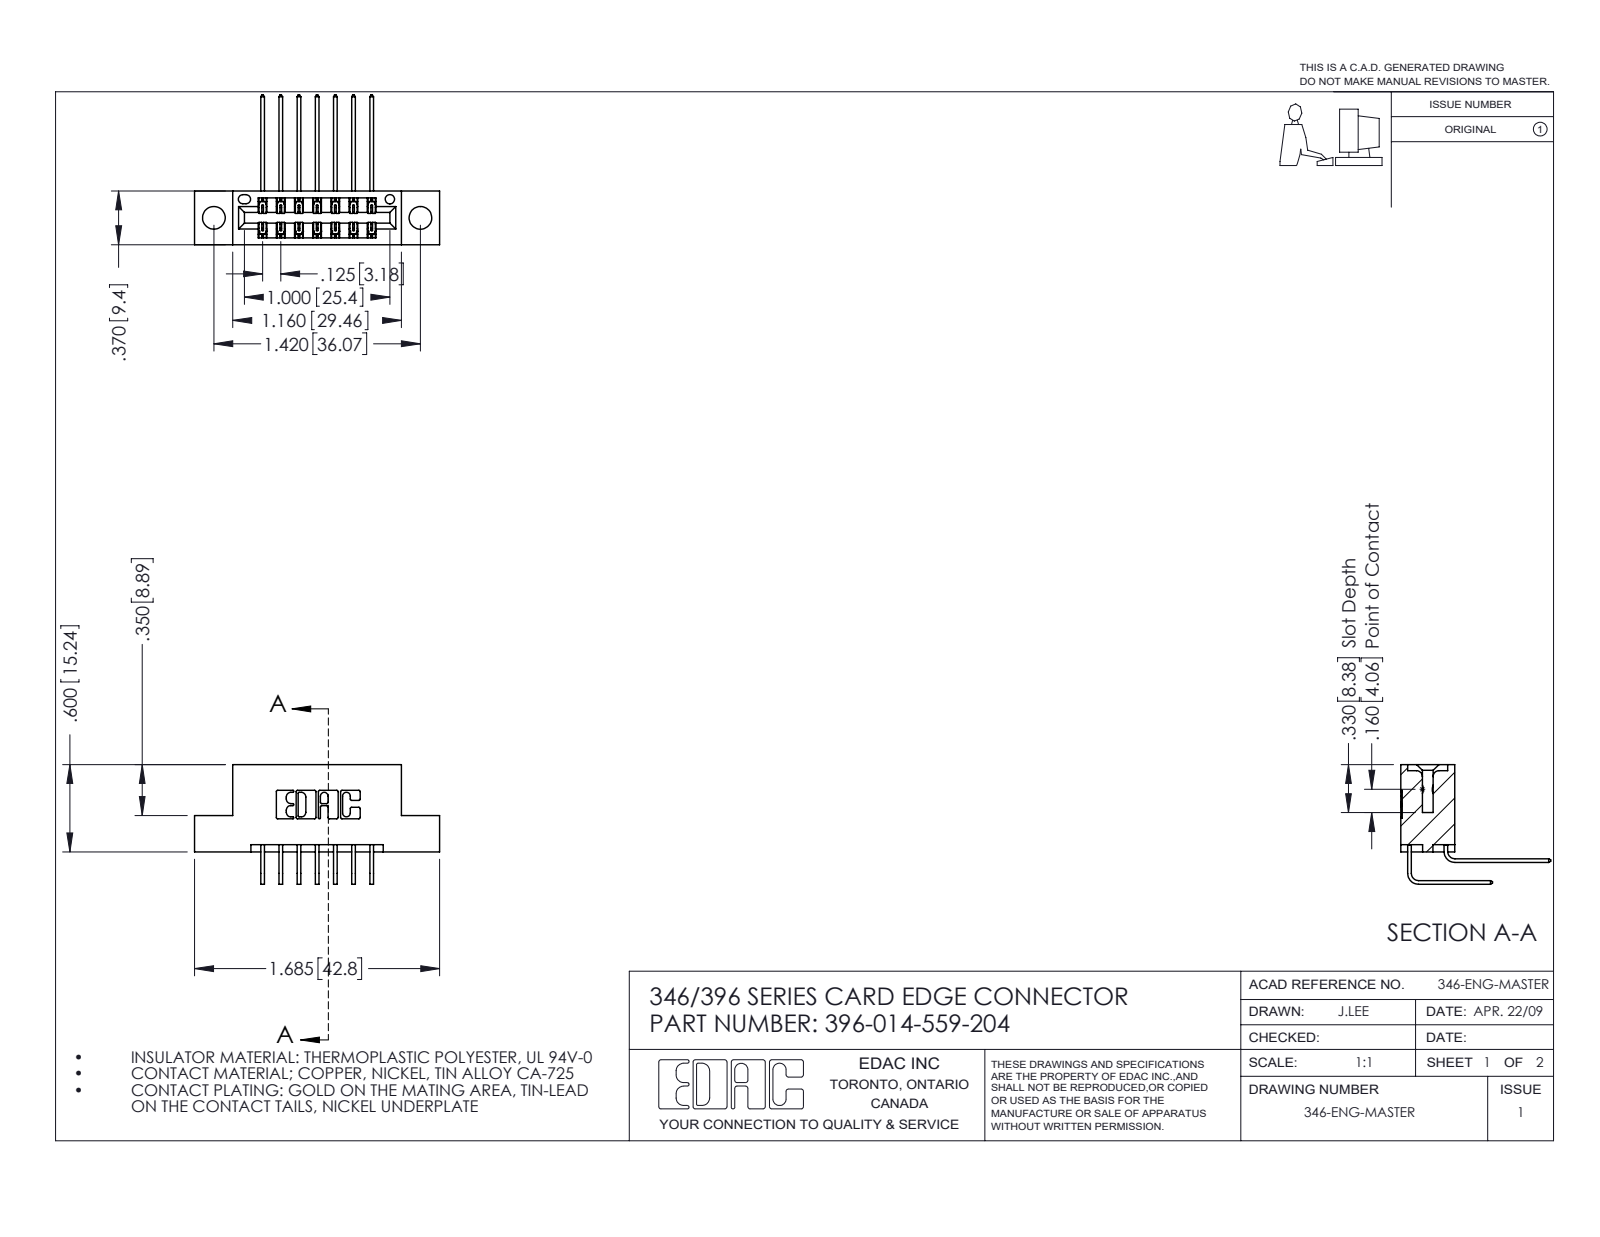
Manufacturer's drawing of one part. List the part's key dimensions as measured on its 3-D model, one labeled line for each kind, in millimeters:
Part name (STEP PRODUCT): 346 Part_Flush Mounting Lugs - 0.156 Dia-TH; 345-292-001_558 559 Tail - 1; 396-014-559-204; 345-292-001_559 Tail - 2
STEP written by: SolidWorks 2016 (CONFIG_CONTROL_DESIGN)
Units: millimetres
Bodies: 15 solids, 878 faces (594 planar, 284 cylindrical, 0 other)
Overall size (bounding box): 42.8 × 26.2 × 20.9
Volume: 3 900 mm³ · Surface area: 5 004 mm²
Round holes (diameter × count): ⌀4 ×2, ⌀1.6 ×1
Partial cylindrical surfaces — rounded edges, fillets, slot ends (radius × count): R0.3 ×22, R0.2 ×21, R0.2 ×6, R0.8 ×6, R0.7 ×3, R0.4 ×2, R0.6 ×2, R0.6 ×2
Main face-to-face distances: 6.4, 1.2, 8.2, 9.4, 0.6, 7.6, 1.8, 3.2, 3.2, 3.8
Hole centre spacings: 6.2, 30.9, 36.1
